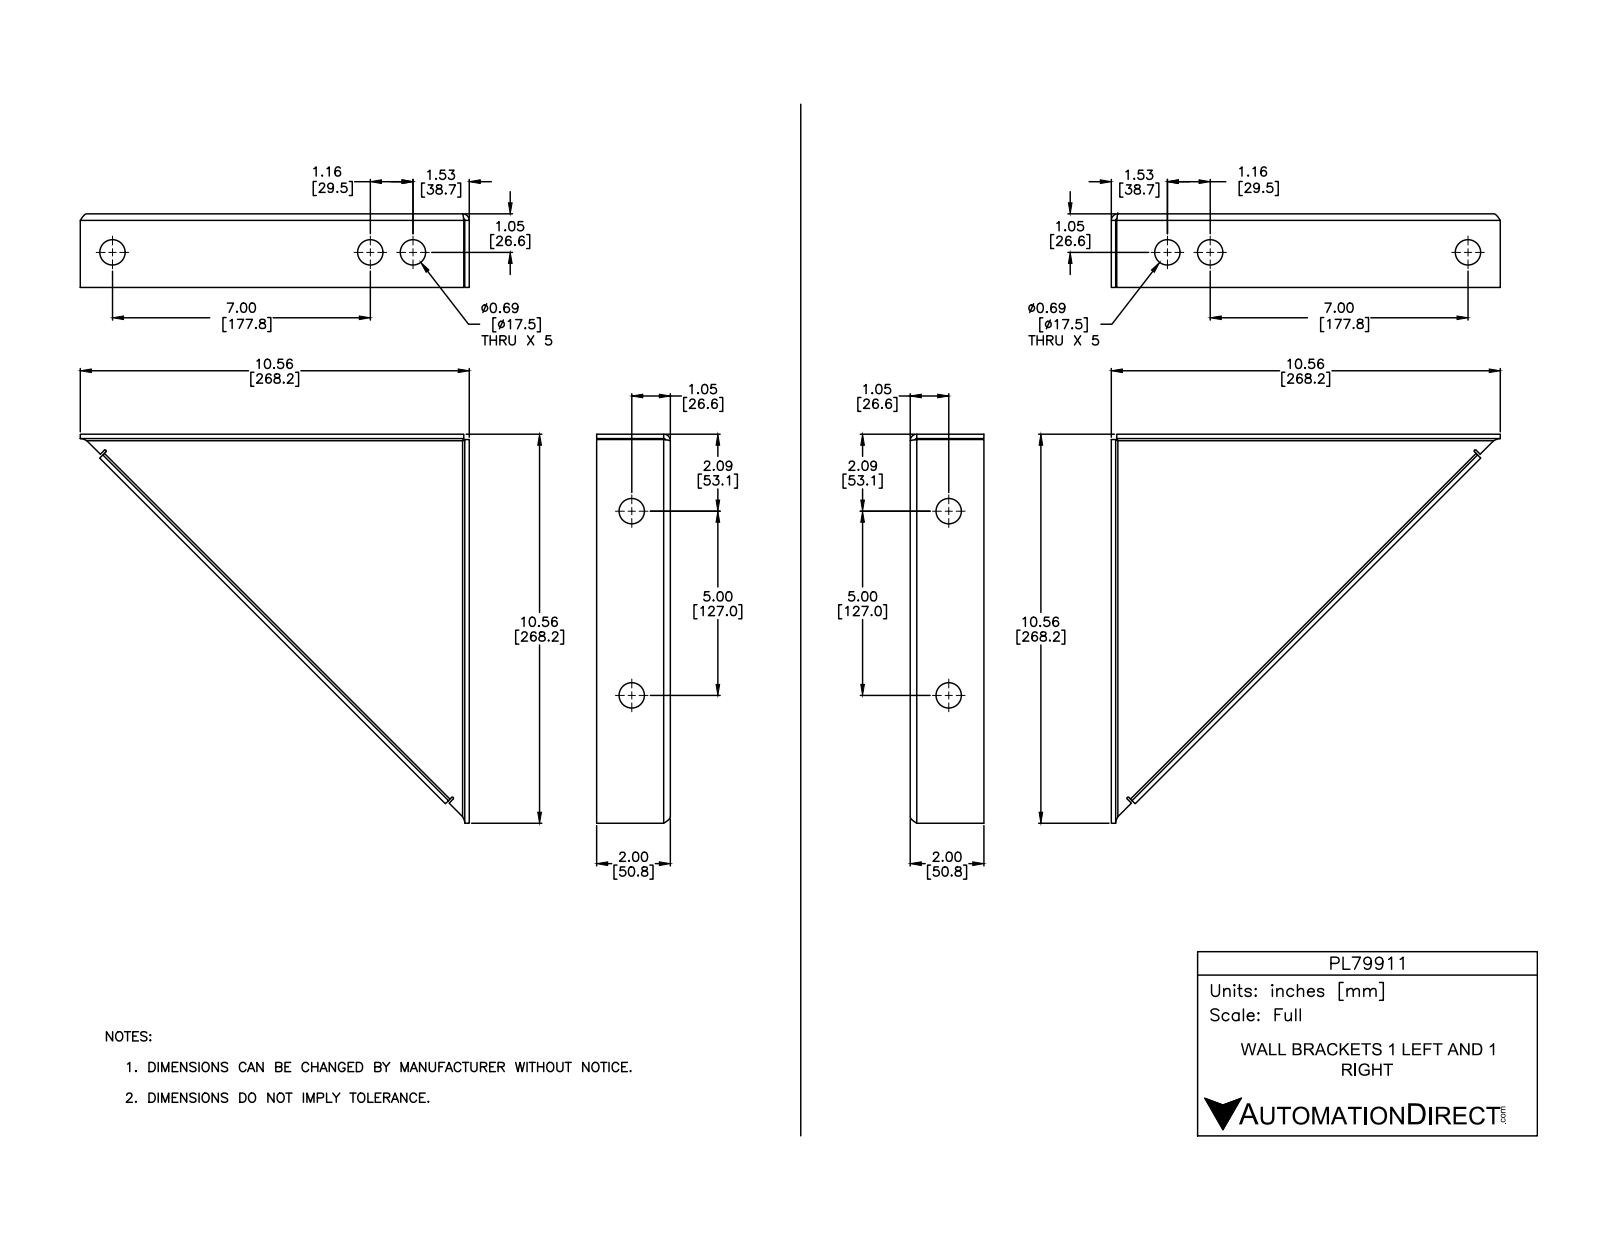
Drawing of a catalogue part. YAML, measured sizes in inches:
part_name: "PL79911_2; PL79911_1; PL79911"
step_written_by: "SolidWorks 2015 (AUTOMOTIVE_DESIGN)"
units: inches
bodies: {solids: 2, faces: 88, planar: 42, cylindrical: 38, other: 8}
overall_size: [15.344, 10.56, 10.56]
volume: 23.3
surface_area: 403
round_holes:
  - {diameter: 0.687, count: 10}
partial_cylinders:
  - {radius: 0.06, count: 6}
  - {radius: 0.18, count: 6}
  - {radius: 0.03, count: 2}
face_to_face_distances: [0.12, 15.224, 0.119, 15.344, 15.104, 2, 13.344, 1.88, 13.224, 0.5]
hole_center_spacings: [13.25, 1.16, 5, 7, 8.16, 13.25, 13.301, 14.162]
